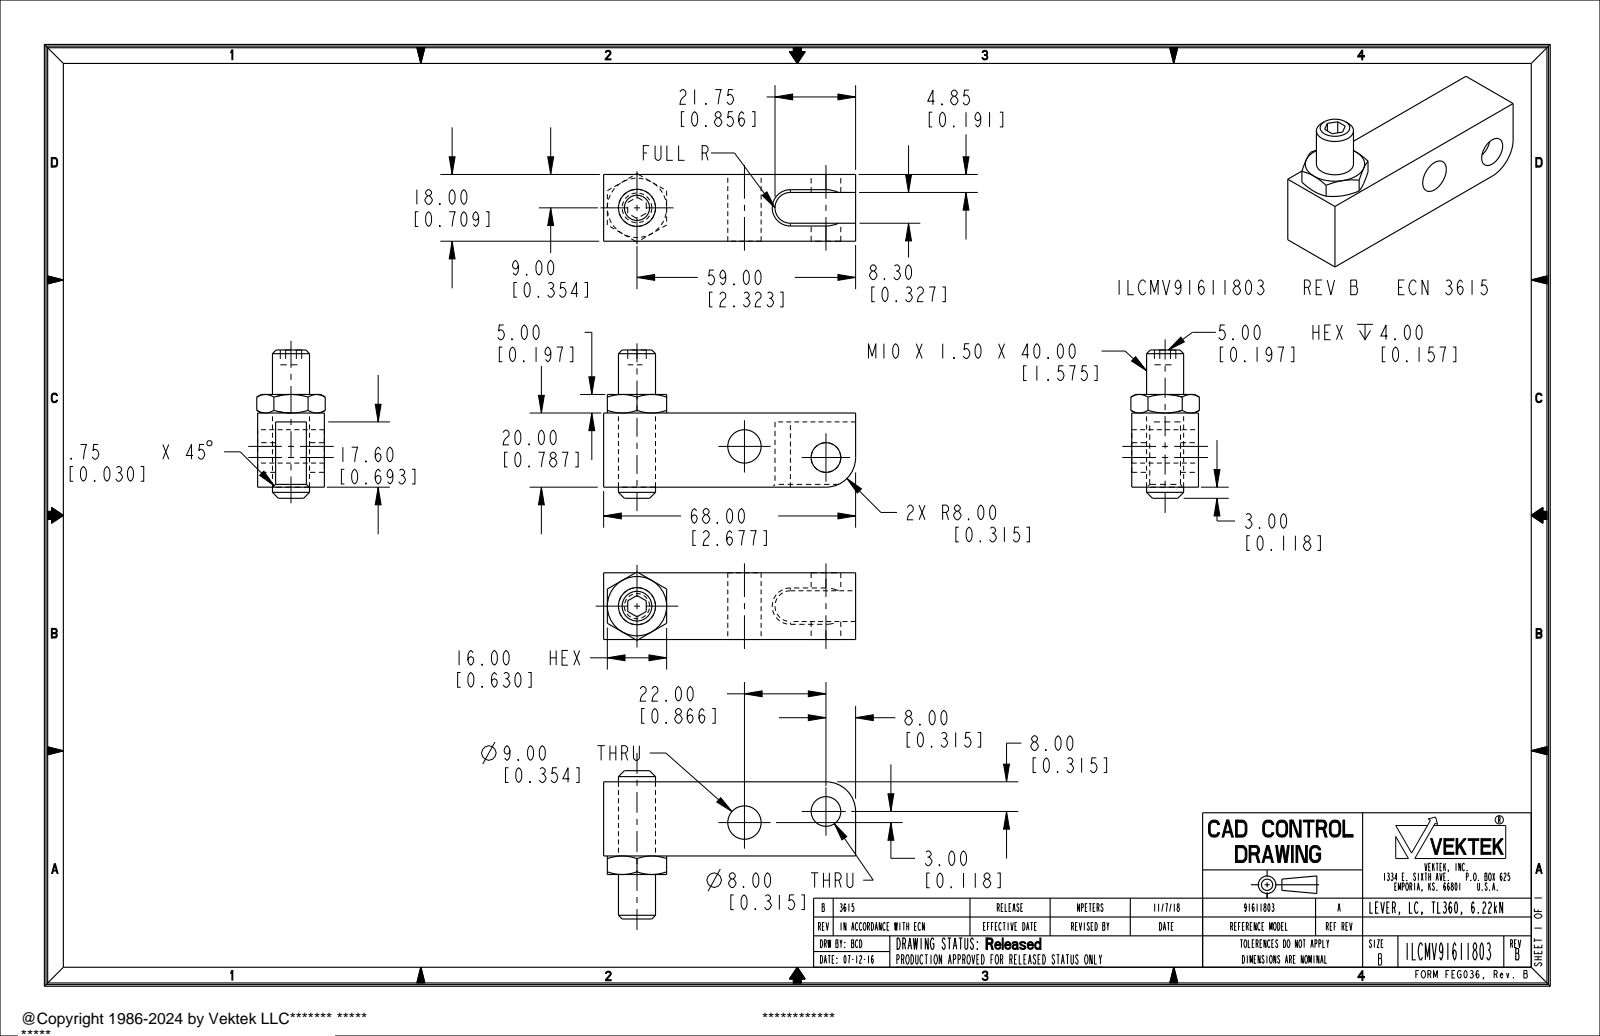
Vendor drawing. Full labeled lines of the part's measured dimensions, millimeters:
Part name (STEP PRODUCT): ILCMV91611803
STEP written by: PRO/ENGINEER BY PARAMETRIC TECHNOLOGY CORPORATION, 2013320 (AUTOMOTIVE_DESIGN)
Units: millimetres
Bodies: 1 solid, 59 faces (27 planar, 15 cylindrical, 17 other)
Overall size (bounding box): 68 × 40 × 18.48
Volume: 21 797 mm³ · Surface area: 8 325 mm²
Round holes (diameter × count): ⌀8 ×1, ⌀9 ×1
Round bosses / shafts (diameter × count): ⌀10 ×1
Partial cylindrical surfaces — rounded edges, fillets, slot ends (radius × count): R4.15 ×1, R8 ×1
Main face-to-face distances: 18, 20, 4.85, 13.15, 8.3, 17.6, 2.4, 5, 68, 16
Hole centre spacings: 22.2
